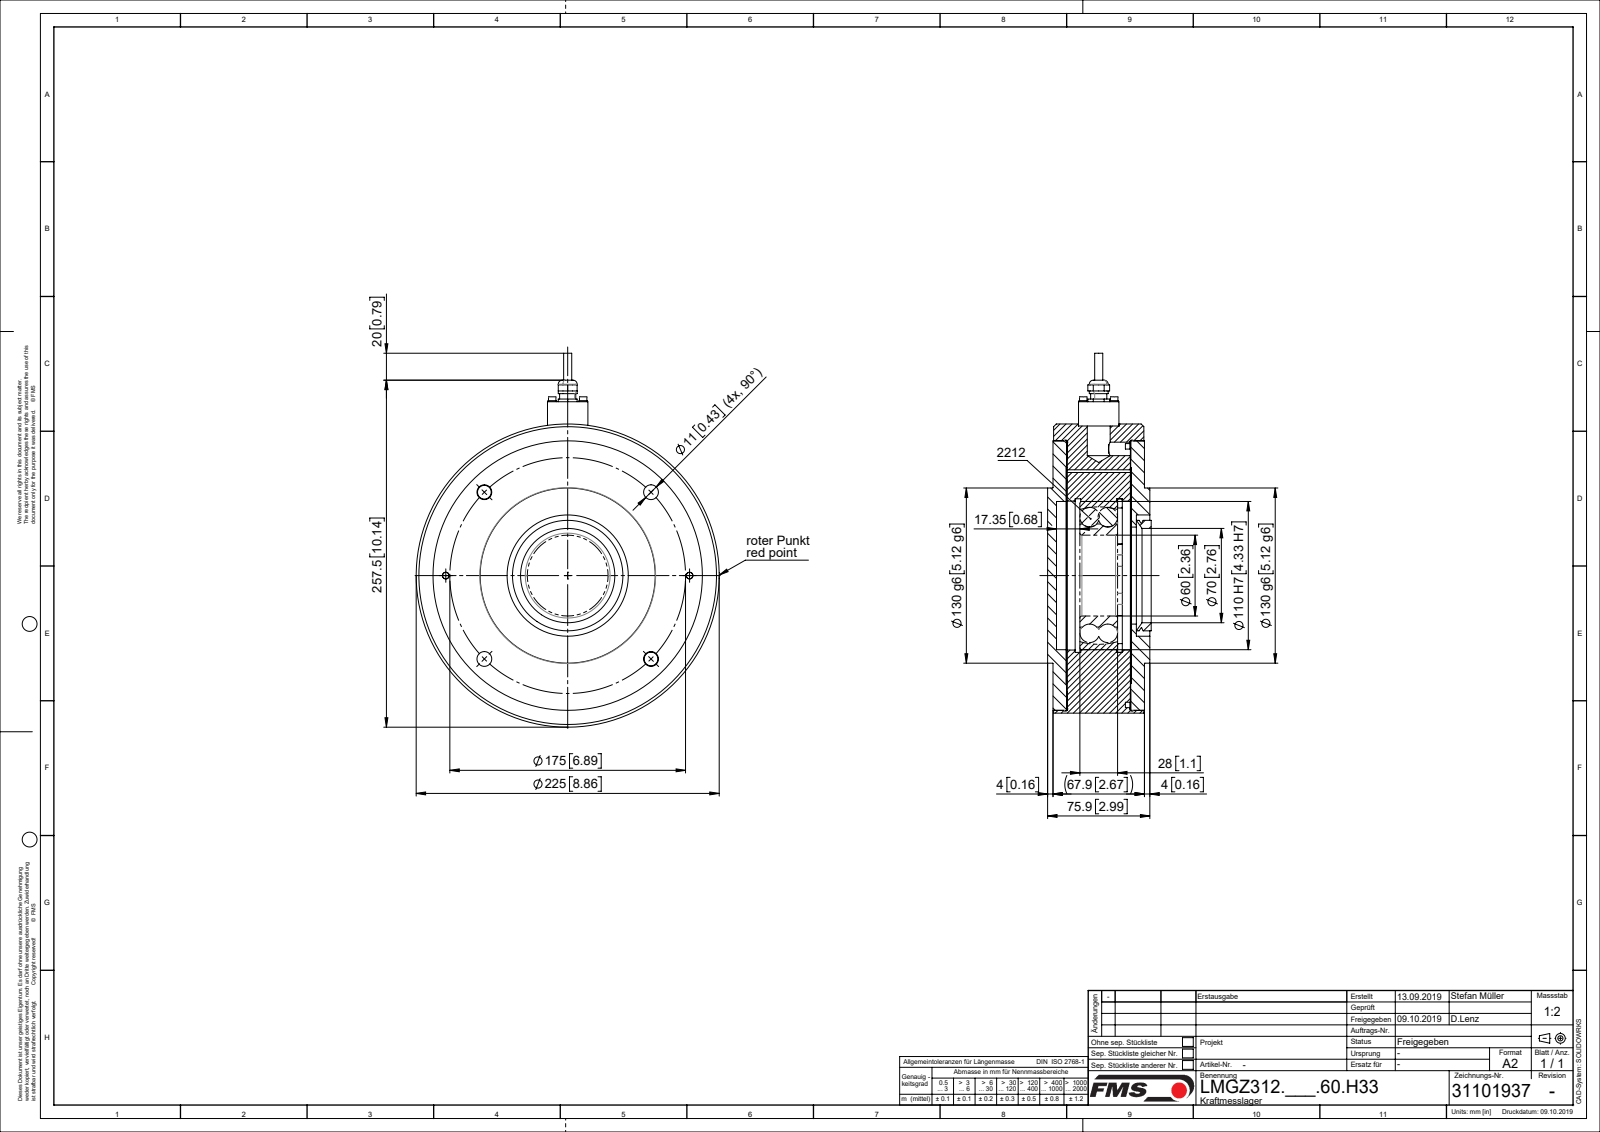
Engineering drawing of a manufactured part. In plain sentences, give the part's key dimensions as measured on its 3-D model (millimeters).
The part is named "ZEICHNUNG3; L50036; L4765504; TEIL1 (+8 more)". Its 3-D file was written by "Mechanical Desktop 2009 (CONFIG_CONTROL_DESIGN)". It is 20 solids with 369 faces: 113 planar, 200 cylindrical and 56 other. Overall it measures 257.5 by 225 by 75.9 millimeters. Its volume is 2 356 000 cubic millimeters and its surface area 385 593 square millimeters. Round holes: 6 of diameter 11, 4 of diameter 2.6, 4 of diameter 3.2, 4 of diameter 3.4, 4 of diameter 9, 2 of diameter 5, 2 of diameter 6.6, 1 of diameter 6, 1 of diameter 11.28, 1 of diameter 23, 1 of diameter 60, 1 of diameter 70. Round bosses or shafts: 4 of diameter 6.2, 4 of diameter 5.5, 4 of diameter 3, 2 of diameter 10, 2 of diameter 6, 1 of diameter 225, 1 of diameter 199, 1 of diameter 130. Partial cylindrical surfaces (rounded edges, fillets, slot ends): 1 of radius 81, 1 of radius 86. The main face-to-face distances are 47.25, 10.45, 10.2, 57.45, 57.7, 47.5, 9.75, 9.7, 58.2, 0.5. The hole center spacings are 16.26, 23, 68.17, 87.5, 123.74, 164.45, 32.53, 90.5.
